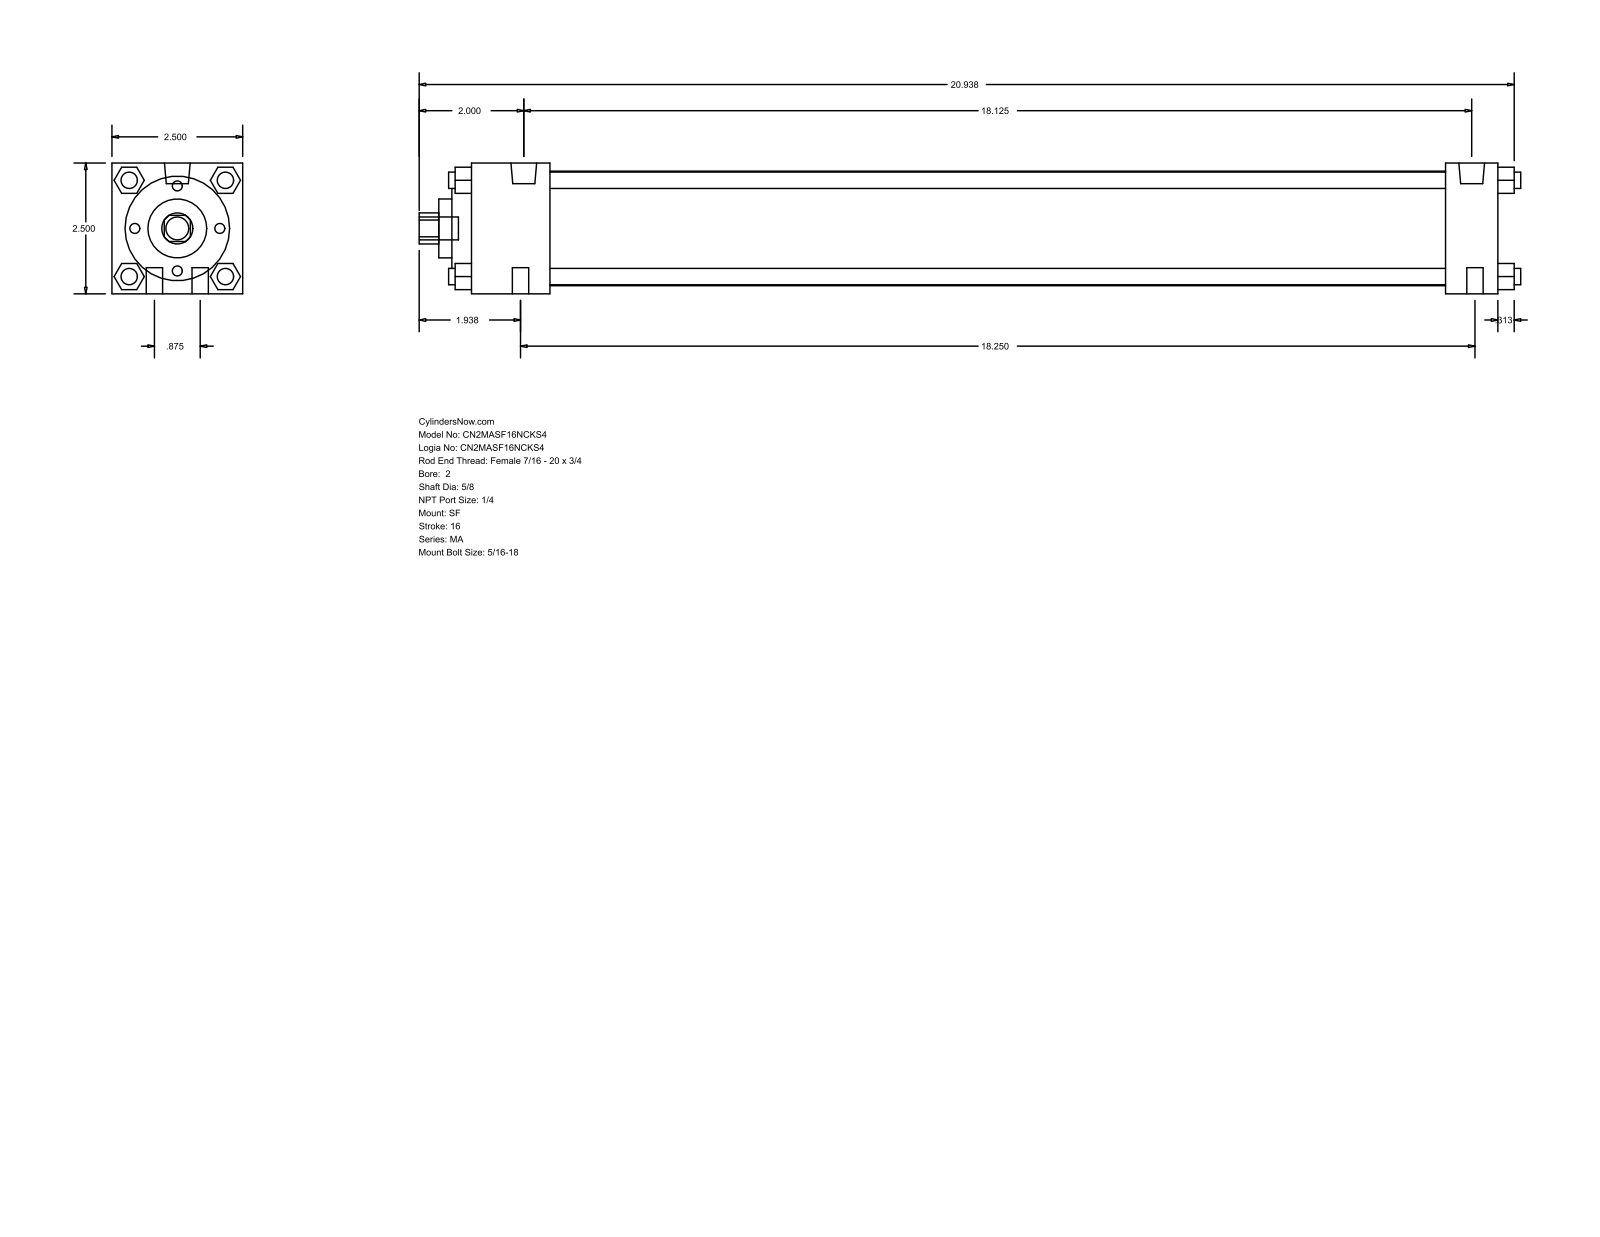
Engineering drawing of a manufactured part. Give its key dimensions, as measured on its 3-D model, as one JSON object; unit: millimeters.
{"part_name": "MA_SF__0200_0.625", "step_written_by": "GSSL Pune (CONFIG_CONTROL_DESIGN)", "units": "millimeters", "bodies": {"solids": 0, "faces": 126, "planar": 95, "cylindrical": 31, "other": 0}, "overall_size": [534.99, 63.5, 63.5], "round_holes": [[15.88, 1], [28.57, 1], [50.8, 1], [55.63, 1]], "round_bosses_or_shafts": [[7.94, 10], [12.49, 2], [11.11, 1]], "partial_cylinders_radius": [[7.54, 1]], "face_to_face_distances": [63.5, 12.7, 25.4, 38.1, 498.48, 9.52, 473.08, 434.98, 460.38, 47.62]}
